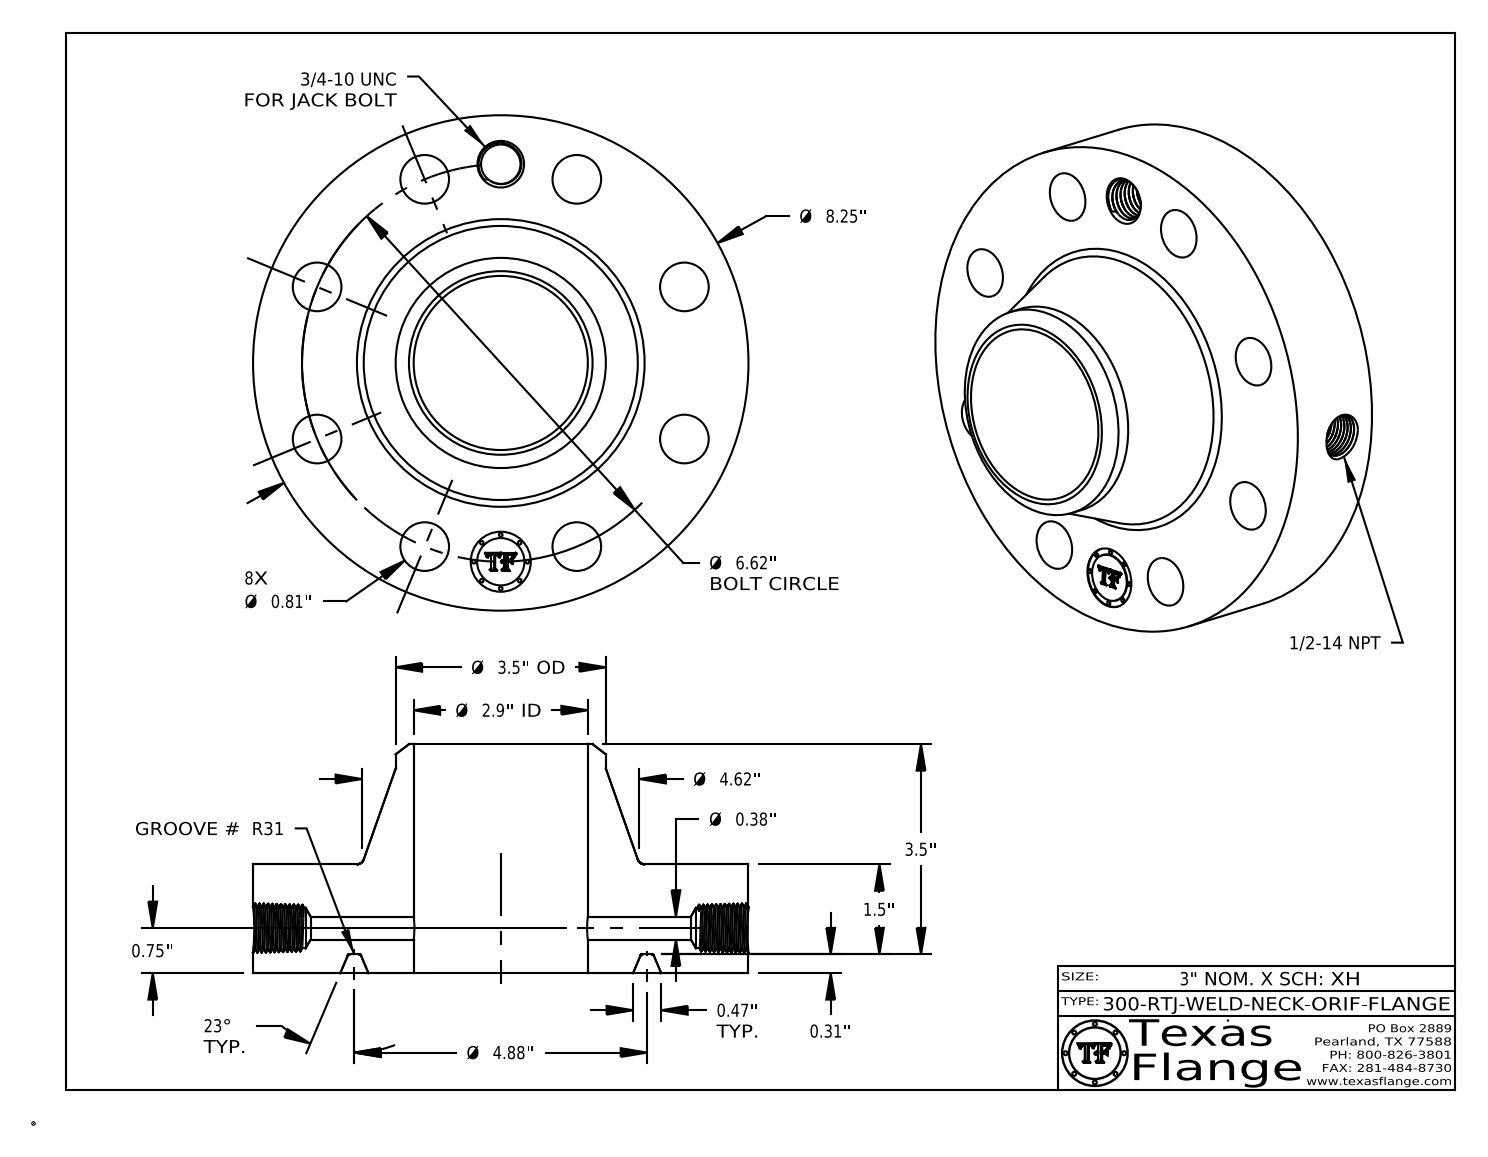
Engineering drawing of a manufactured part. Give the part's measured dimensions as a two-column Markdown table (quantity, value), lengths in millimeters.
| quantity | value |
| --- | --- |
| part name | 300-RTJ-WELD-NECK |
| STEP written by | CATIA V5 STEP AP214 (AUTOMOTIVE_DESIGN) |
| units | millimeters |
| bodies | 1 solid, 795 faces (370 planar, 96 cylindrical, 329 other) |
| overall size | 209.6 × 209.6 × 96.9 |
| volume | 1 397 000 mm³ |
| surface area | 156 800 mm² |
| round holes (diameter × count) | 20.6 × 8, 9.7 × 1, 16.7 × 1, 17.1 × 1, 25.4 × 1, 73.7 × 1 |
| round bosses / shafts (diameter × count) | 1.5 × 8, 209.6 × 1, 88.9 × 1, 20 × 1 |
| main face-to-face distances | 46.1, 8, 38.1, 96.9, 88.9, 50.8, 0.4, 45.7, 37.7, 51.2 |
| hole center spacings | 84.1, 118.9, 155.3, 168.1, 32.8, 64.3, 64.3, 93.4 |
